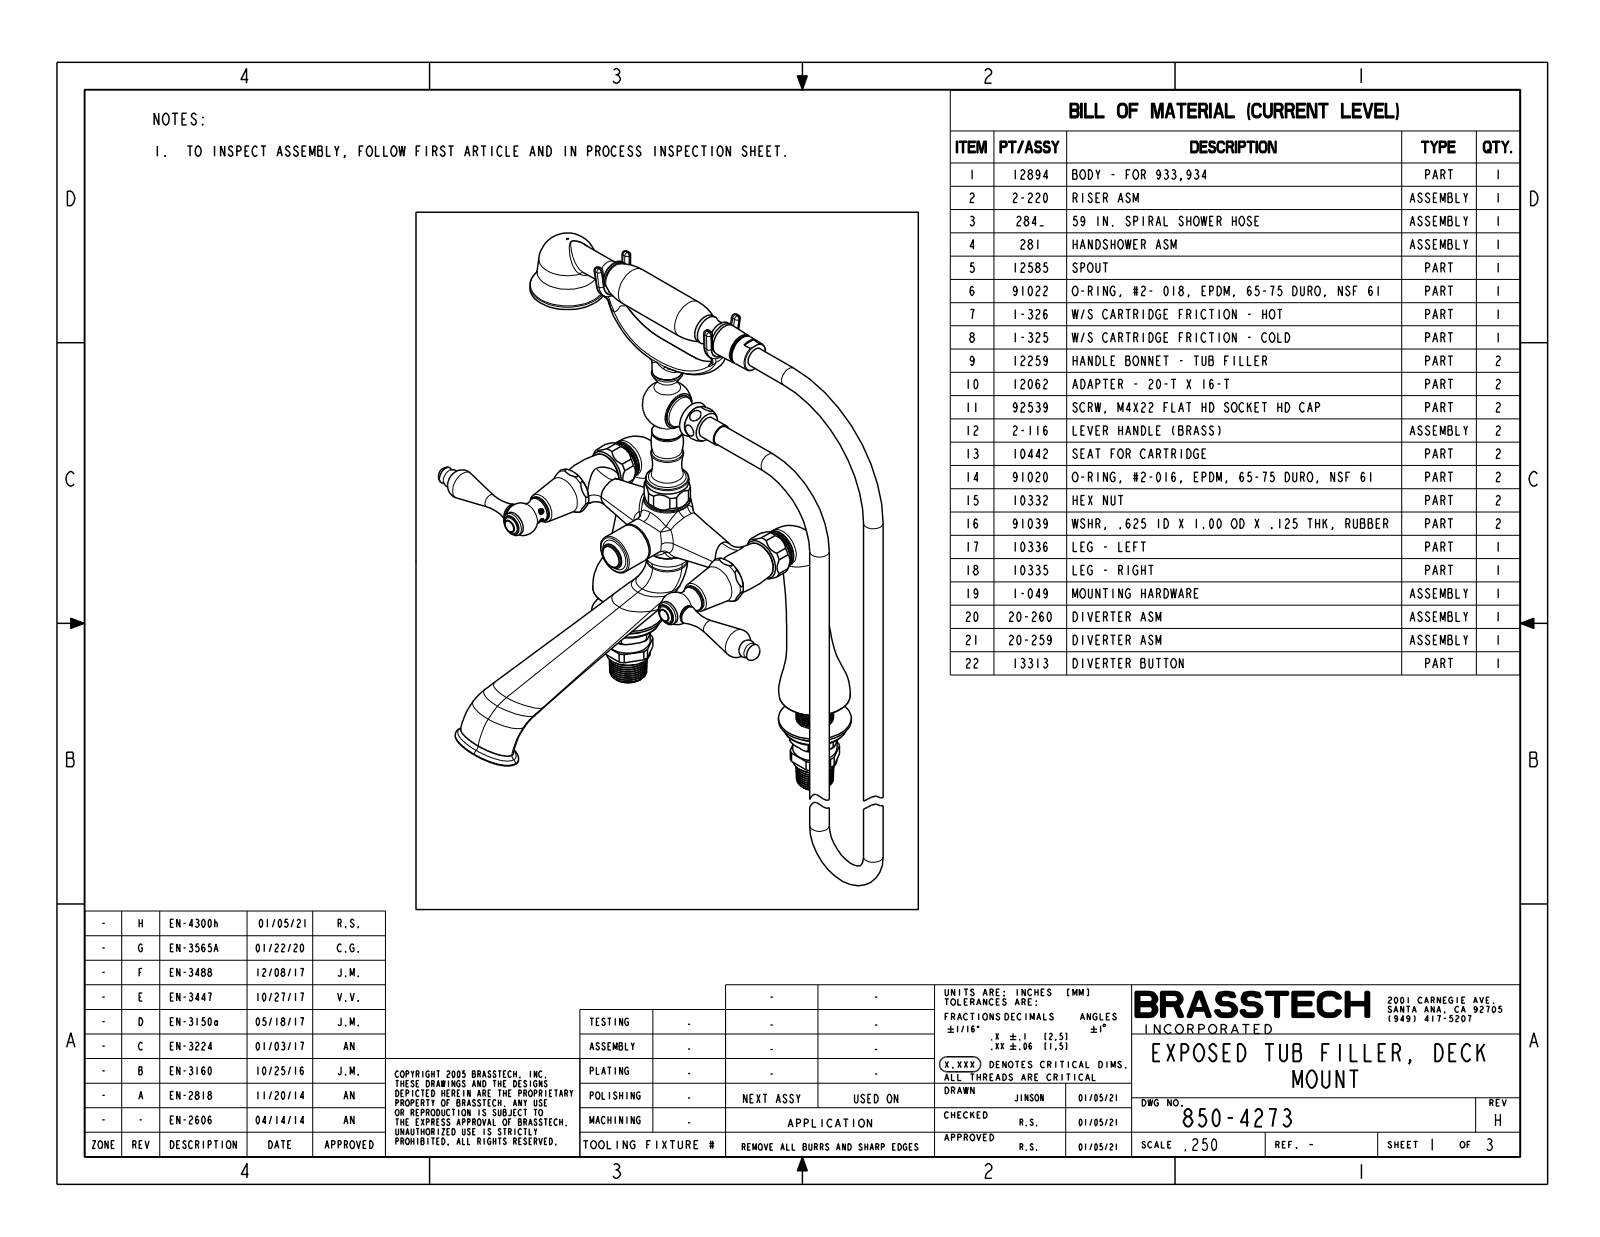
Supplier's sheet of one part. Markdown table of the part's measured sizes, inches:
| quantity | value |
| --- | --- |
| part name | 850-4273 |
| STEP written by | CREO PARAMETRIC BY PTC INC, 2018400 (CONFIG_CONTROL_DESIGN) |
| units | inches |
| bodies | 1 solid, 853 faces (179 planar, 239 cylindrical, 435 other) |
| overall size | 23.86 × 14.41 × 10.575 |
| volume | 61.26 in³ |
| surface area | 297 in² |
| round holes (diameter × count) | 0.046 × 52 |
| round bosses / shafts (diameter × count) | 0.82 × 4, 0.54 × 4, 1.02 × 2, 0.705 × 2, 0.661 × 2, 0.544 × 2, 0.4 × 2, 2.08 × 1 |
| partial cylindrical surfaces (radius × count) | 0.085 × 32, 0.637 × 3, 0.595 × 2, 0.405 × 1, 0.406 × 1, 0.45 × 1 |
| main face-to-face distances | 1.188, 0.982, 3, 4.188, 1.812, 11.04, 10.058, 1.31, 0.58, 2.576 |
| hole center spacings | 0.187, 0.367, 0.535, 0.813, 1.021, 0.184, 0.601, 0.685 |
